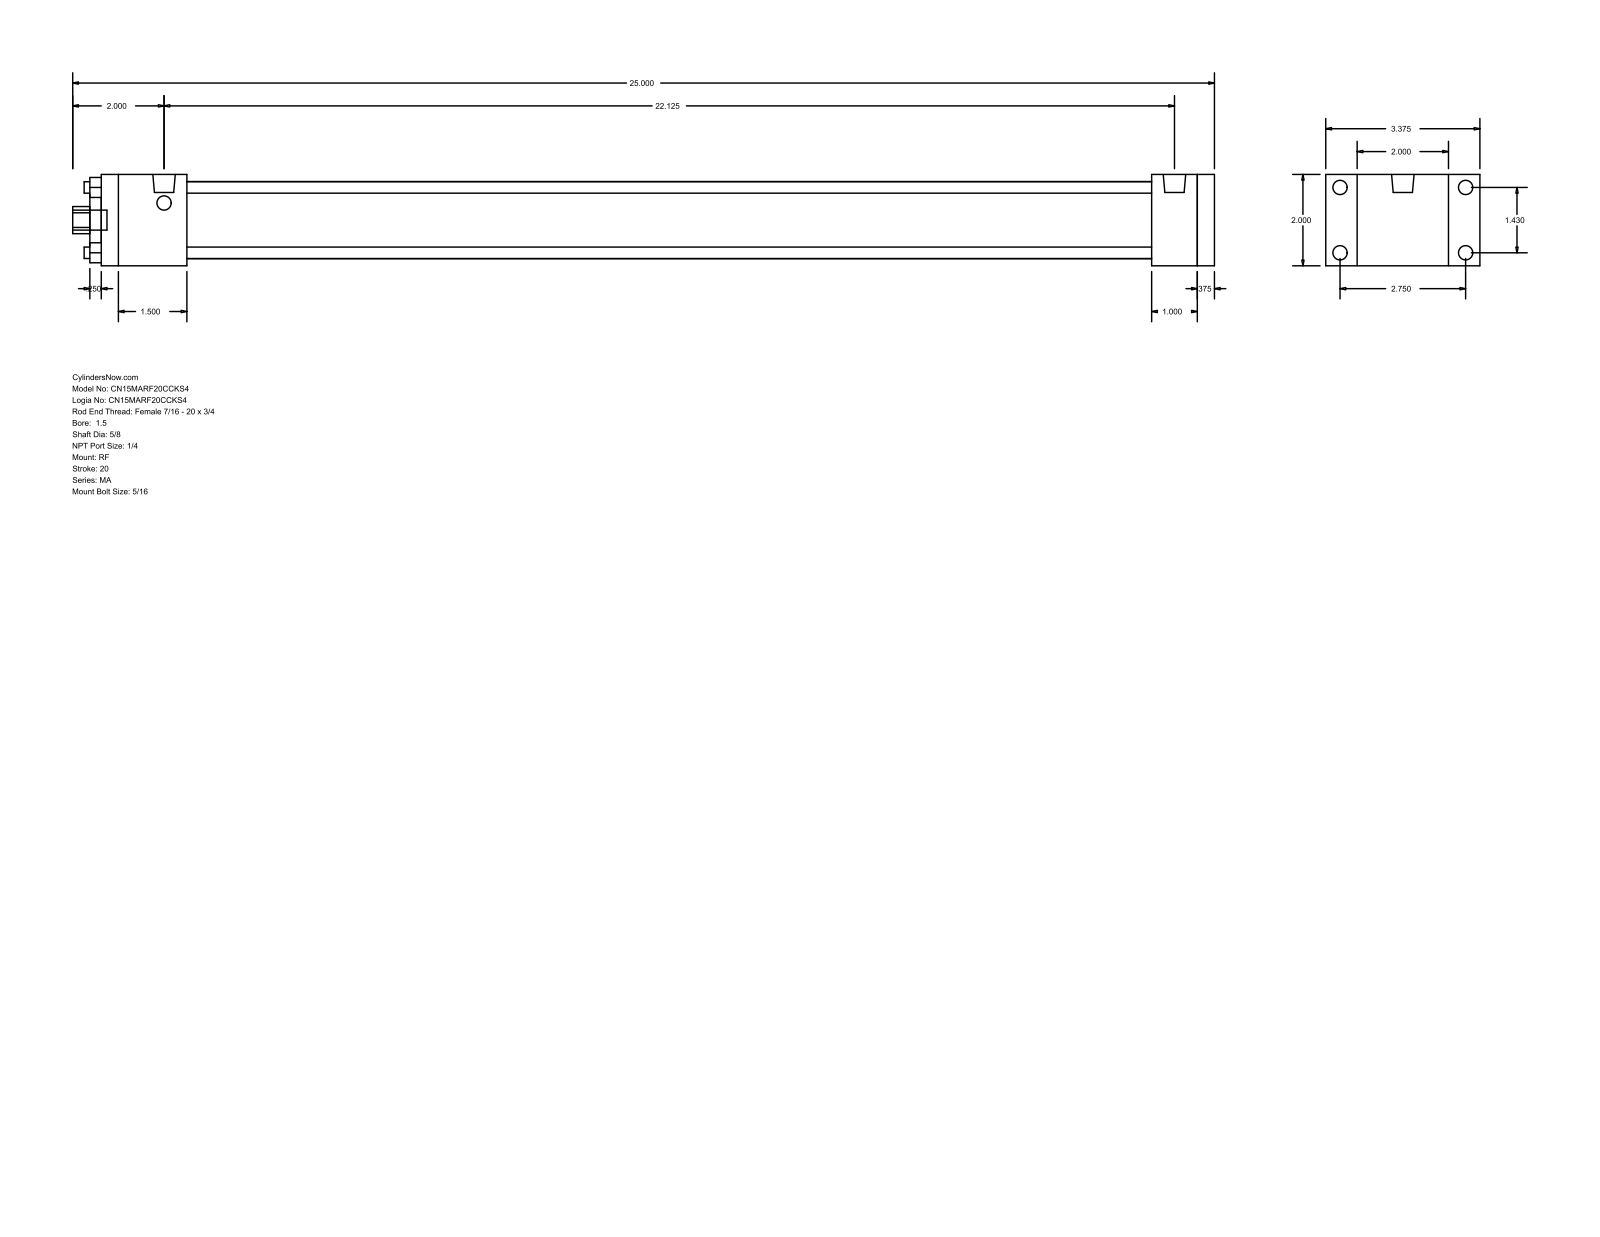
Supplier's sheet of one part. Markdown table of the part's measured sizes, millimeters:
| quantity | value |
| --- | --- |
| part name | MA_RF__0150_0.625 |
| STEP written by | GSSL Pune (CONFIG_CONTROL_DESIGN) |
| units | millimeters |
| bodies | 0 solids, 92 faces (64 planar, 28 cylindrical, 0 other) |
| overall size | 635 × 85.72 × 50.8 |
| round holes (diameter × count) | 6.35 × 4, 15.88 × 1, 28.57 × 1, 42.93 × 1 |
| round bosses / shafts (diameter × count) | 7.94 × 8, 12.49 × 2, 11.11 × 1 |
| partial cylindrical surfaces (radius × count) | 7.54 × 1 |
| main face-to-face distances | 50.8, 9.52, 609.6, 619.12, 584.2, 25.4, 34.92, 47.62, 536.58, 561.98 |
| hole center spacings | 25.68, 36.32, 51.36 |
